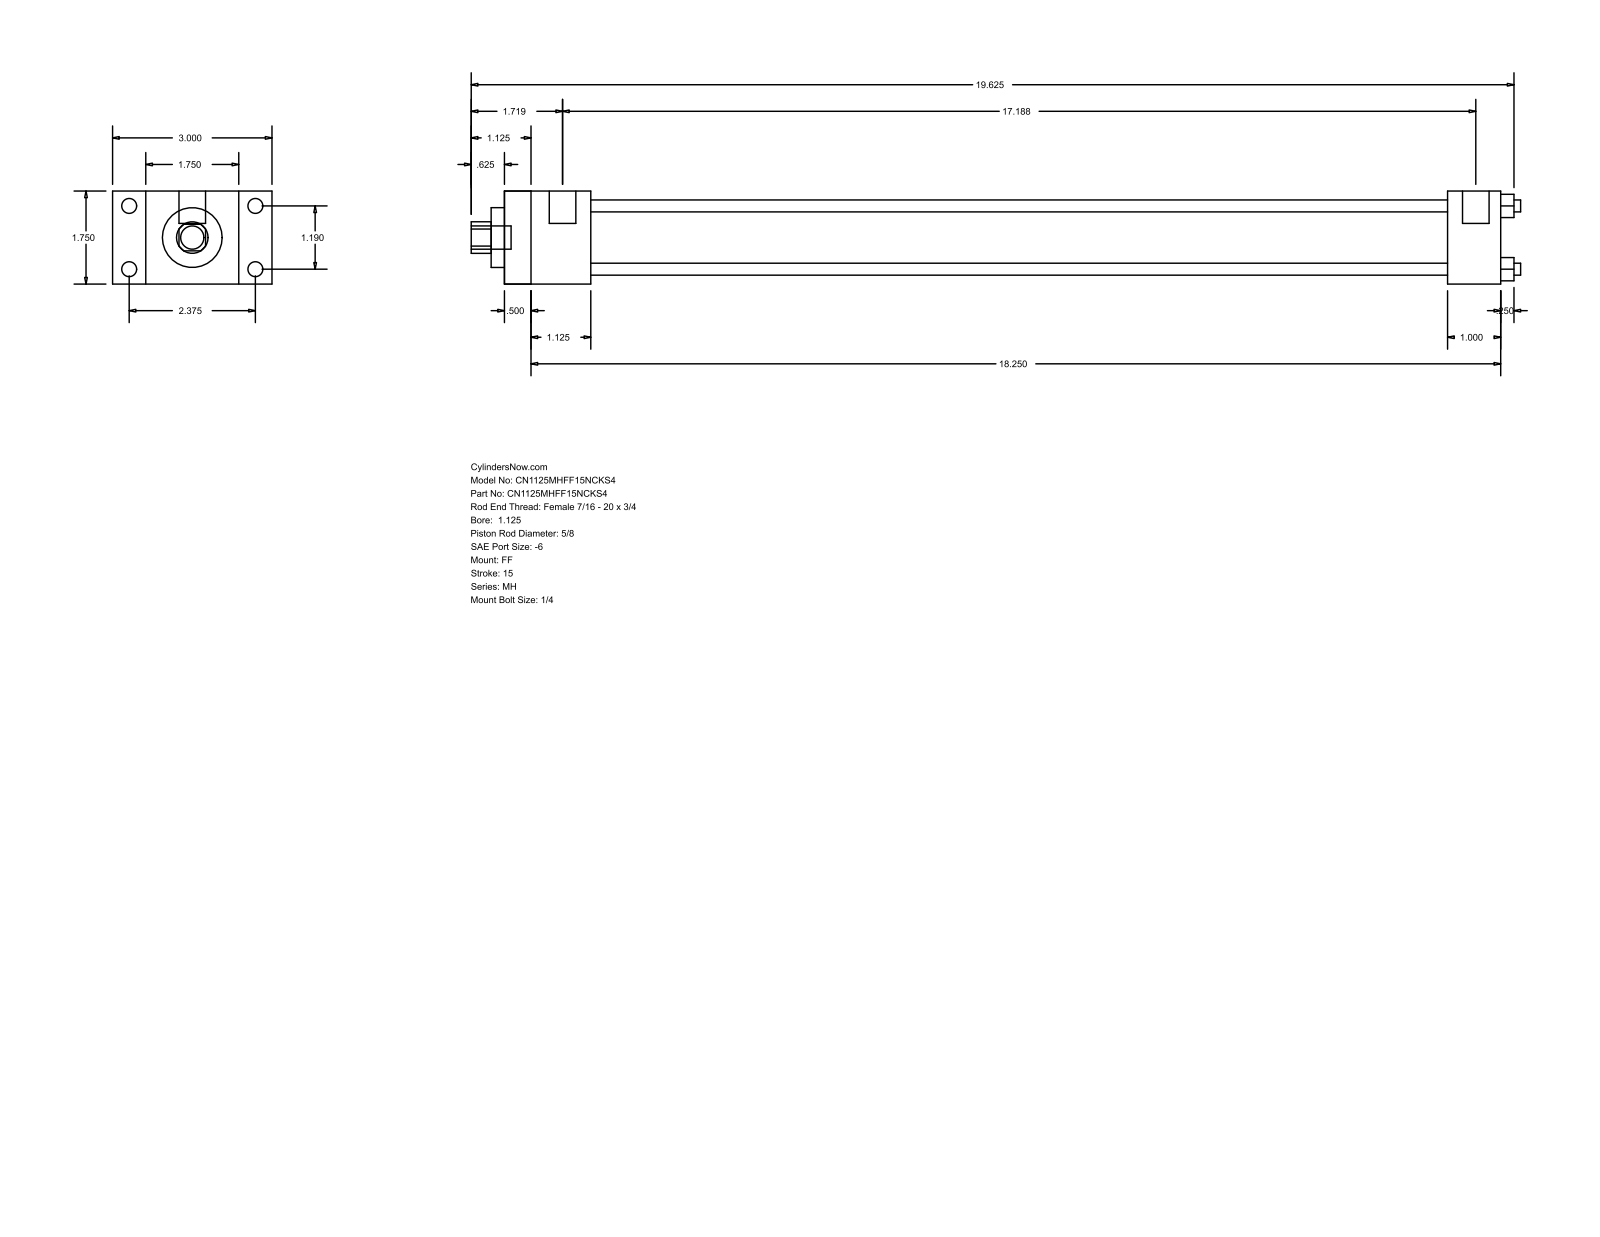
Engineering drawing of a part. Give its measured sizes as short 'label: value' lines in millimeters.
name: MH_FF__0112_0.625
written by: GSSL Pune (CONFIG_CONTROL_DESIGN)
unit: mm
bodies: 0 solids, 92 faces (64 planar, 28 cylindrical, 0 other)
size: 501.65 × 76.2 × 44.45
holes: 4× ⌀5.71, 1× ⌀15.88, 1× ⌀28.57, 1× ⌀34.92
bosses: 4× ⌀7.14, 4× ⌀5.56, 2× ⌀12.7, 1× ⌀11.11
rounds: 1× R7.54
face distances: 44.46, 476.24, 15.87, 12.69, 463.55, 60.33, 28.58, 41.27, 450.85, 438.16
hole spacings: 21.37, 30.22, 42.74
